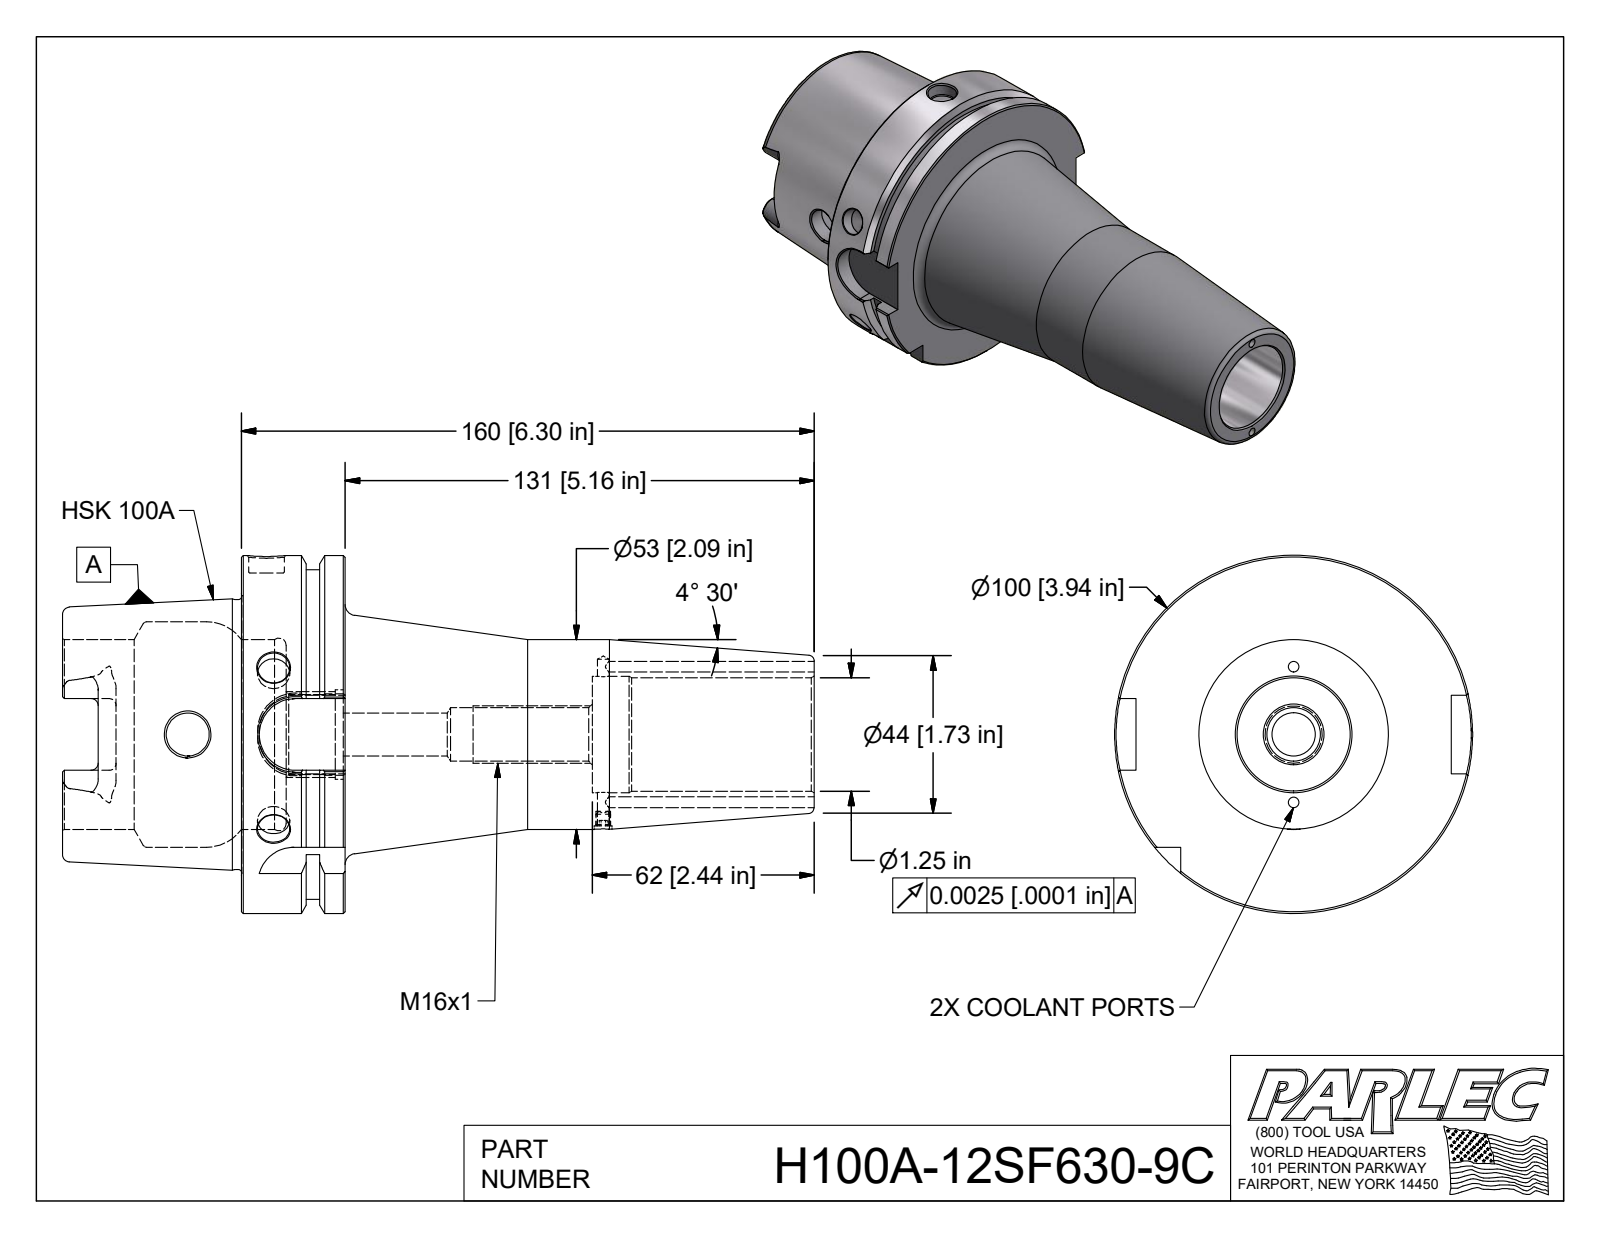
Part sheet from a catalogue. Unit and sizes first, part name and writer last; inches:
Units: inches
Overall size (bounding box): 8.269 × 3.937 × 3.937
Round holes (diameter × count): ⌀0.118 ×2, ⌀0.354 ×2, ⌀0.472 ×2, ⌀0.128 ×1, ⌀0.197 ×1, ⌀0.394 ×1, ⌀0.587 ×1, ⌀0.881 ×1, ⌀0.985 ×1, ⌀1.248 ×1, ⌀1.278 ×1, ⌀2.087 ×1
Round bosses / shafts (diameter × count): ⌀3.937 ×1, ⌀3.622 ×1, ⌀2.967 ×1
Partial cylindrical surfaces — rounded edges, fillets, slot ends (radius × count): R0.079 ×6, R0.192 ×4, R0.394 ×4
Main face-to-face distances: 1.142, 0.492, 0.65, 1.969, 2.461, 3.11, 5.828, 3.859, 3.367, 2.717
Hole centre spacings: 0.745, 1.49, 3.704
Volume: 30.24 in³ · Surface area: 124.2 in²
Bodies: 1 solid, 150 faces (49 planar, 42 cylindrical, 59 other)
STEP written by: Autodesk Inventor 2018 (AUTOMOTIVE_DESIGN)
